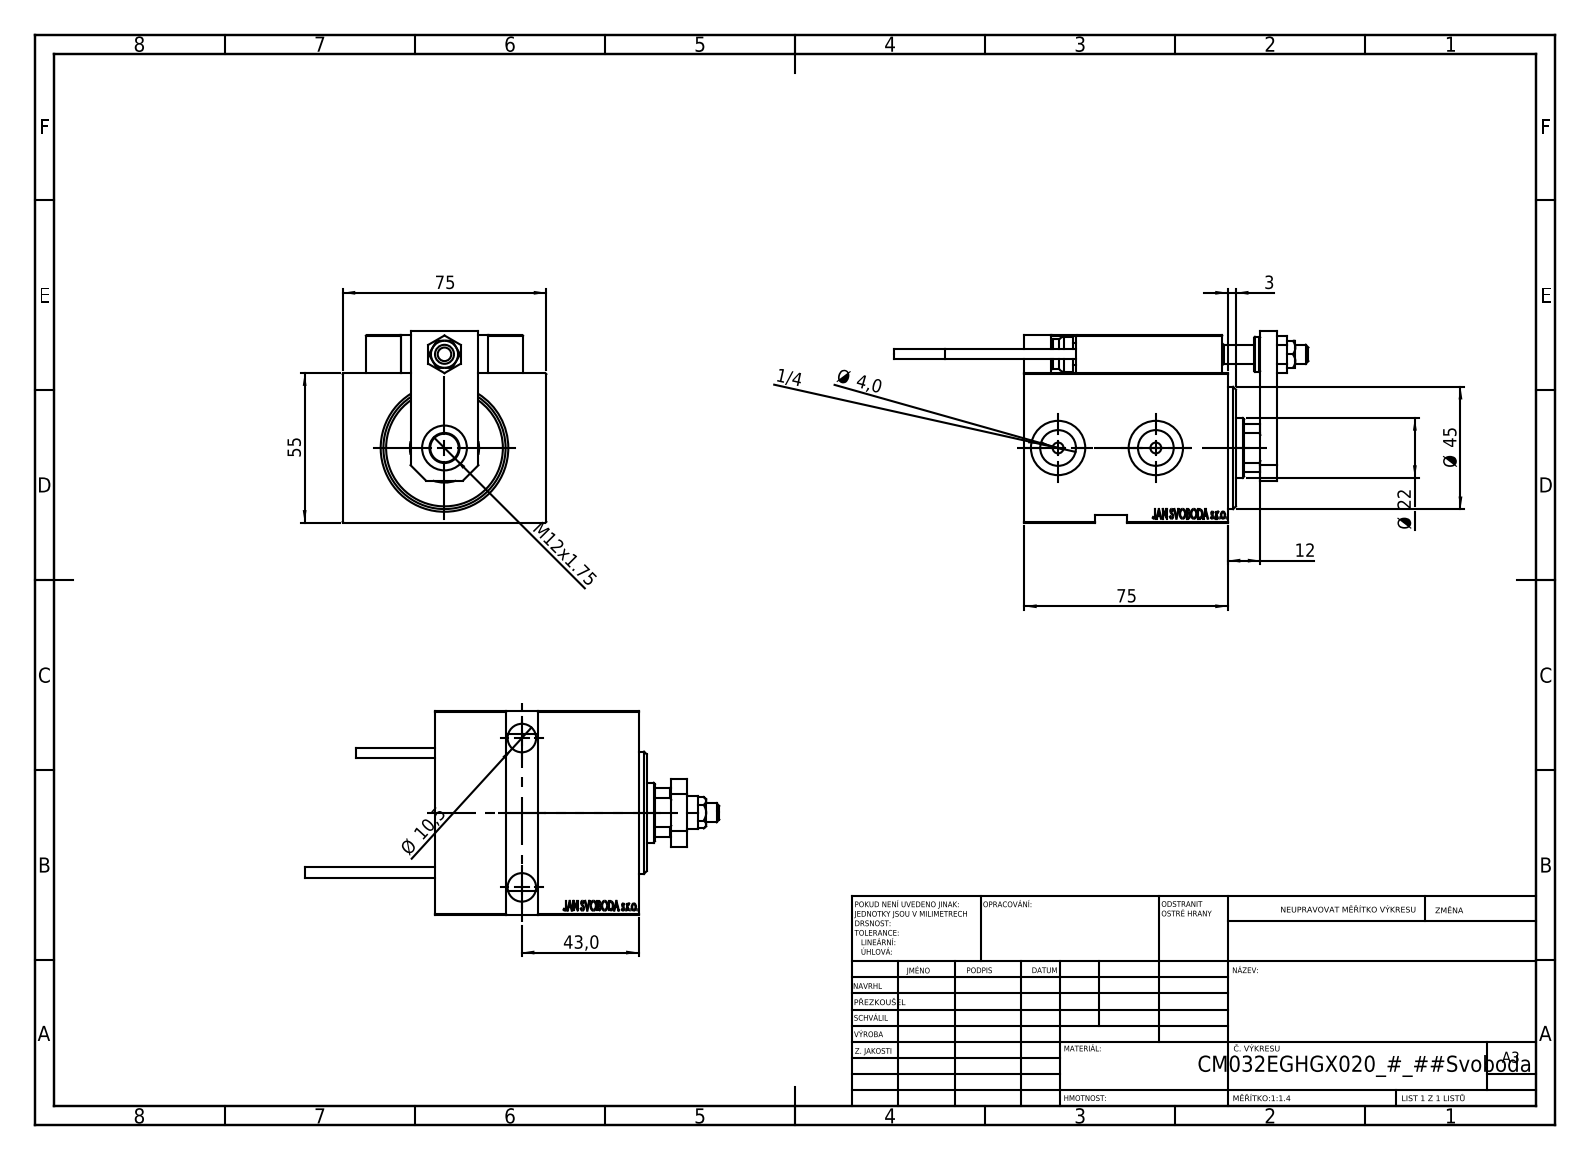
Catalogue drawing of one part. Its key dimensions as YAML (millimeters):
part_name: "V450CM_E_Body; V450CM_E_VCP; TYC_L79; Block (+7 more)"
step_written_by: "SolidWorks 2019 (CONFIG_CONTROL_DESIGN)"
units: millimeters
bodies: {solids: 24, faces: 1280, planar: 567, cylindrical: 172, other: 541}
overall_size: [152.7, 75, 70.5]
volume: 333866
surface_area: 77449
round_holes:
  - {diameter: 4, count: 6}
  - {diameter: 8, count: 5}
  - {diameter: 3.2, count: 4}
  - {diameter: 10.5, count: 3}
  - {diameter: 16.5, count: 3}
  - {diameter: 5, count: 2}
  - {diameter: 13.16, count: 2}
  - {diameter: 20, count: 2}
  - {diameter: 7, count: 1}
  - {diameter: 22, count: 1}
  - {diameter: 25.5, count: 1}
  - {diameter: 32, count: 1}
round_bosses_or_shafts:
  - {diameter: 5, count: 2}
  - {diameter: 3.8, count: 2}
  - {diameter: 34, count: 1}
  - {diameter: 13, count: 1}
  - {diameter: 11, count: 1}
partial_cylinders:
  - {radius: 0.3, count: 30}
  - {radius: 3, count: 2}
  - {radius: 10.5, count: 1}
face_to_face_distances: [75, 55, 3, 10, 12, 14, 25, 65, 7, 5]
hole_center_spacings: [11.37, 20, 27.07, 29.59, 29.69, 32.18, 34.83, 36.06]
